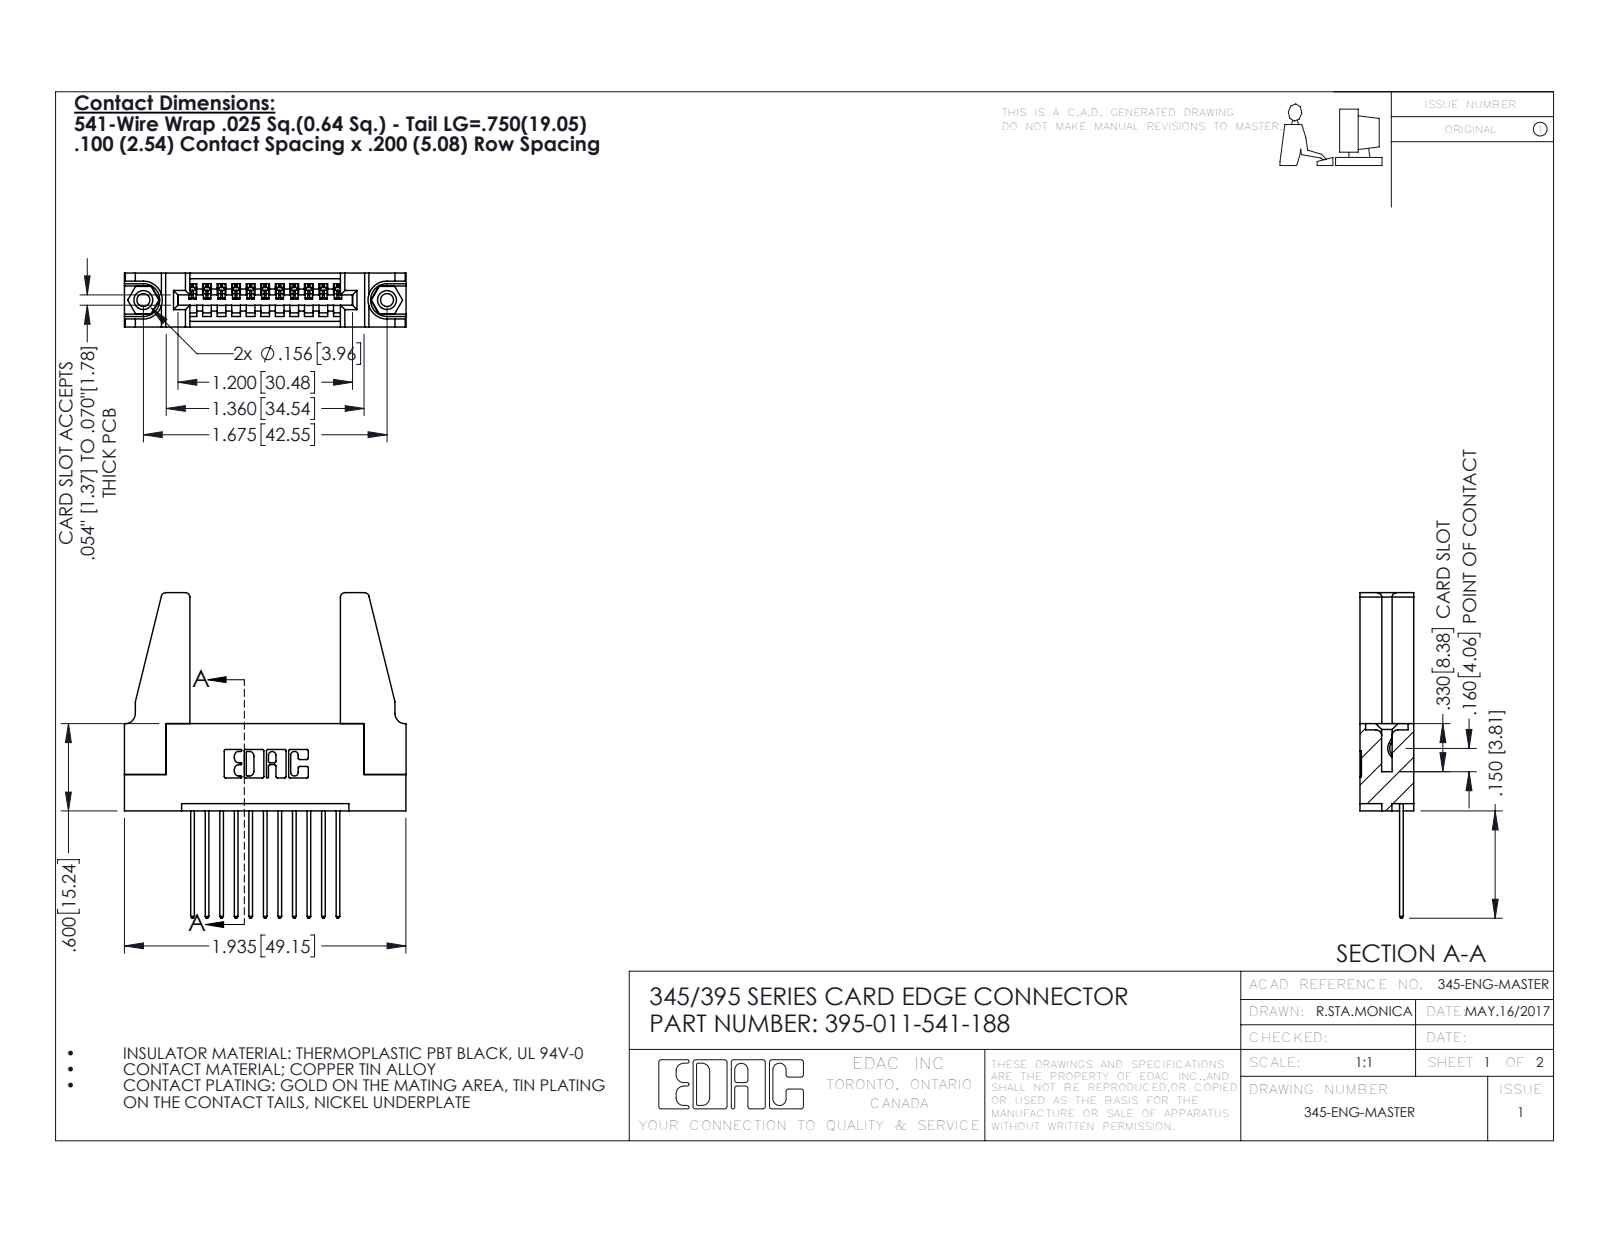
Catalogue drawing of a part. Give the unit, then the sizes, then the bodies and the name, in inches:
Units: inches
Overall size (bounding box): 2.237 × 1.936 × 0.37
Round holes (diameter × count): ⌀0.089 ×2, ⌀0.125 ×2, ⌀0.156 ×2, ⌀0.064 ×1
Round bosses / shafts (diameter × count): ⌀0.155 ×2
Partial cylindrical surfaces — rounded edges, fillets, slot ends (radius × count): R0.006 ×22, R0.01 ×22, R0.01 ×22, R0.03 ×8, R0.007 ×6, R0.031 ×6, R0.026 ×3, R0.031 ×2
Main face-to-face distances: 0.37, 0.072, 0.298, 0.2, 0.098, 0.272, 0.025, 0.225, 0.148, 0.15
Hole centre spacings: 0.27, 1.443, 1.675
Volume: 0.47 in³ · Surface area: 13.7 in²
Bodies: 16 solids, 888 faces (592 planar, 280 cylindrical, 16 other)
Part name (STEP PRODUCT): 345-220-078_345-220-088; 345-292-001_345-293-141; 395-011-541-188; 345-250-001_345-250-001-102 (+1 more)
STEP written by: SolidWorks 2016 (CONFIG_CONTROL_DESIGN)
